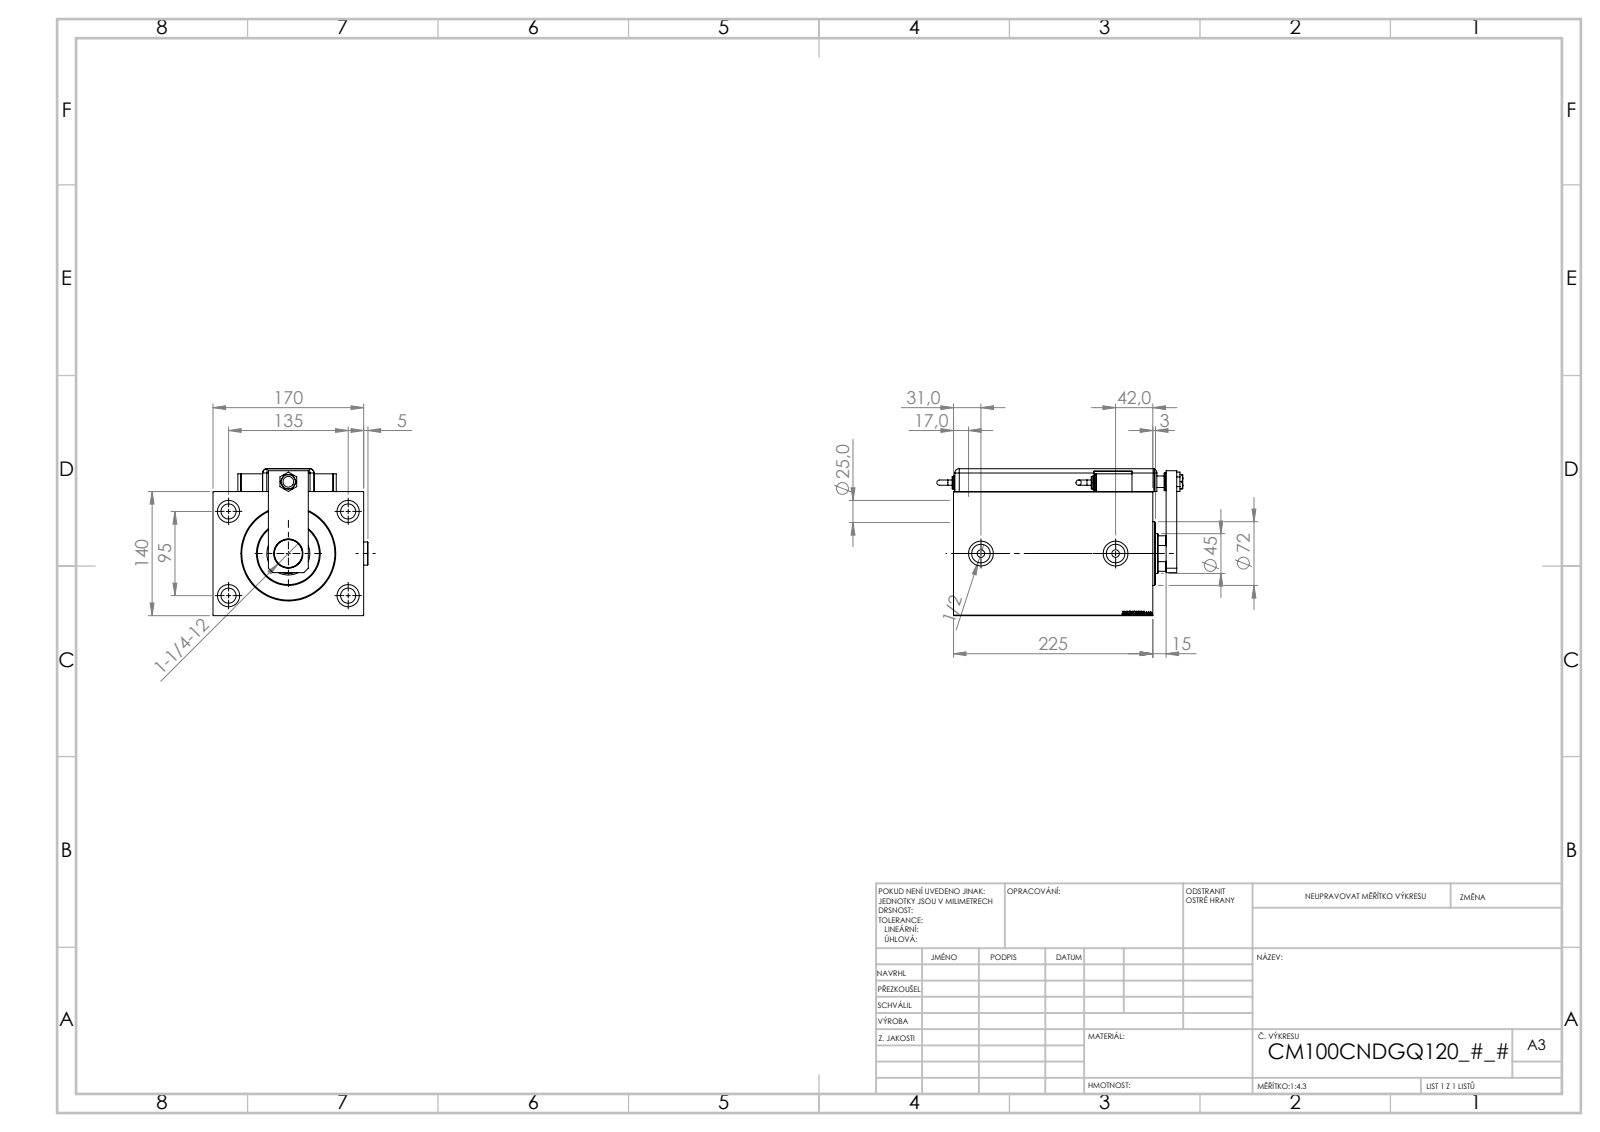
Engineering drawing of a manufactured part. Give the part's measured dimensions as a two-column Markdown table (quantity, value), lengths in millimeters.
| quantity | value |
| --- | --- |
| part name | V450CM_C_VCP; ZARAZKA_Q; MAGNETIC SWITCH Q; NUT_D13 (+7 more) |
| STEP written by | SolidWorks 2019 (CONFIG_CONTROL_DESIGN) |
| units | millimeters |
| bodies | 15 solids, 1303 faces (649 planar, 133 cylindrical, 521 other) |
| overall size | 277.66 × 174.9 × 165.8 |
| volume | 4 577 000 mm³ |
| surface area | 483 701 mm² |
| round holes (diameter × count) | 17 × 4, 25 × 4, 4 × 2, 8 × 2, 8.5 × 2, 20.96 × 2, 28 × 2, 12 × 1, 13 × 1, 14 × 1, 31.5 × 1, 33 × 1 |
| round bosses / shafts (diameter × count) | 20 × 3, 26 × 2, 16 × 2, 14 × 2, 6 × 2, 72 × 1 |
| partial cylindrical surfaces (radius × count) | 5 × 9, 10 × 1, 22 × 1 |
| main face-to-face distances | 140, 170, 3, 225, 26, 199, 15, 25.8, 165.8, 162.8 |
| hole center spacings | 82.54, 75.36, 95, 135, 145.15, 165.08, 20, 81 |
